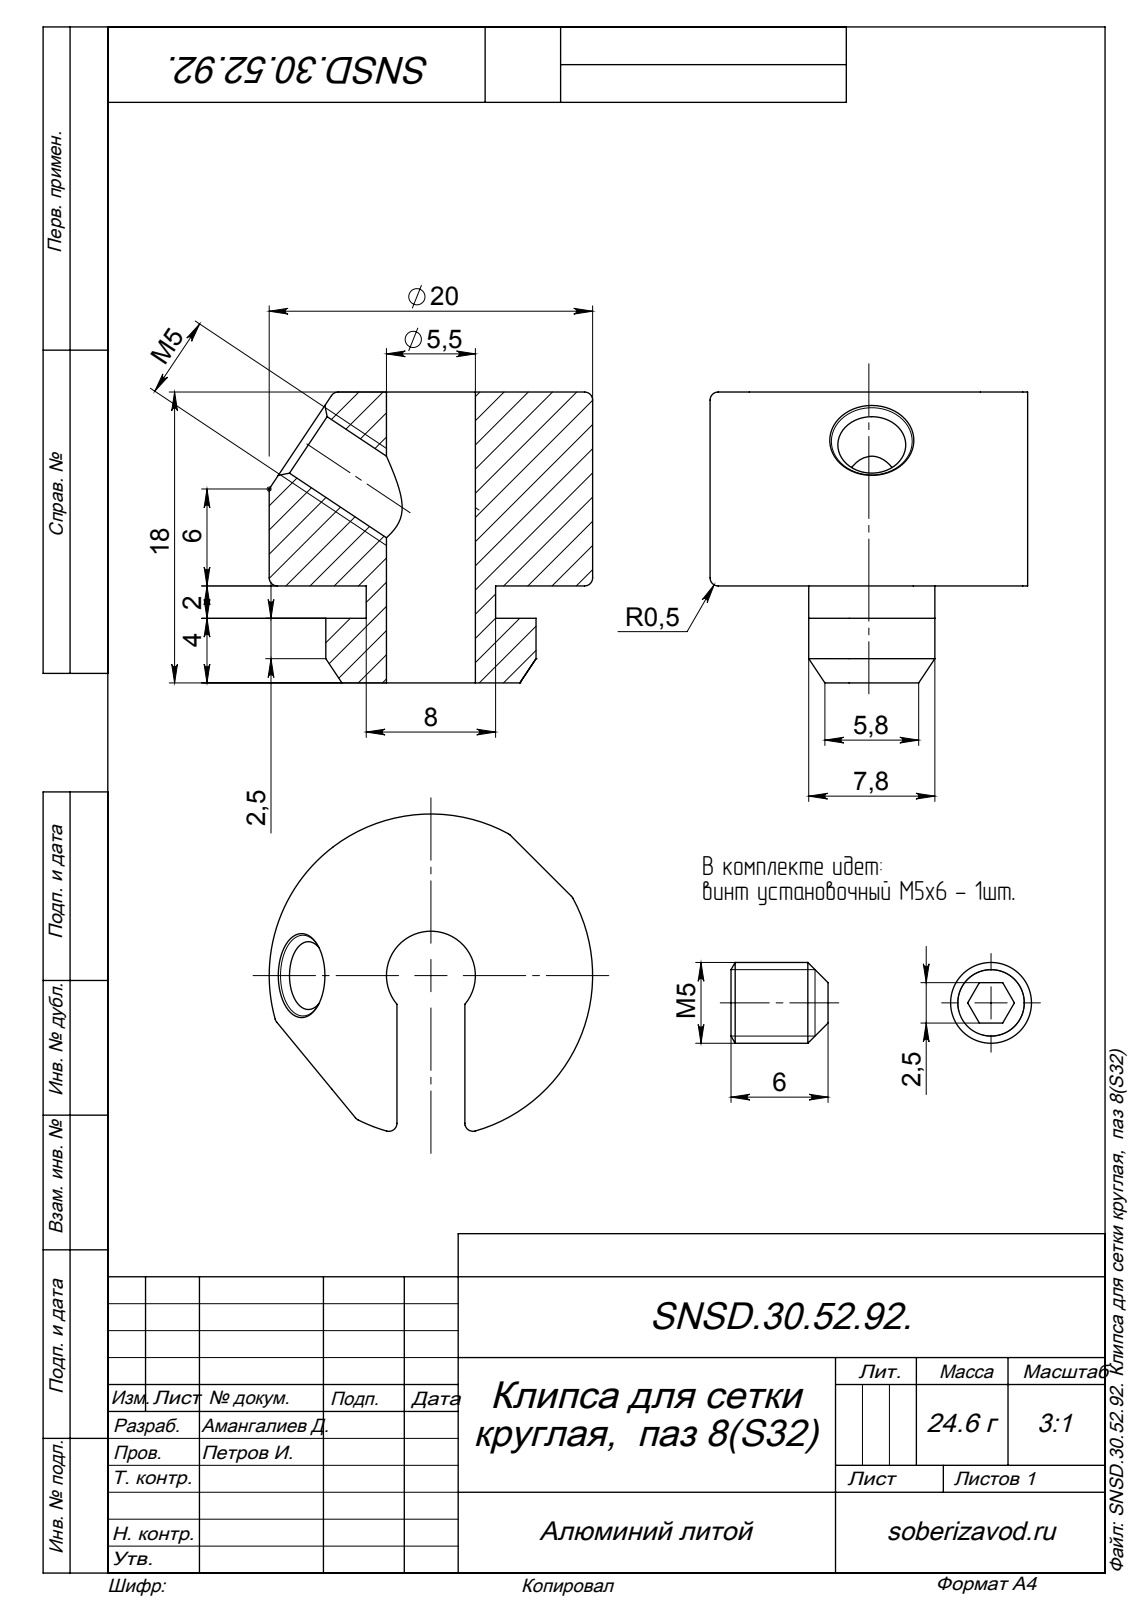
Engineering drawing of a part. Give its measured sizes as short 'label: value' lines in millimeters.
name: Установочный винт23; SNSD.30.52.92. Клипса для сетки круглая, паз 8(S32); socket set screw cup point_din; socket set screw cup point_din_DIN 916 - M5 x 6-C
written by: SolidWorks 2014 (AUTOMOTIVE_DESIGN)
unit: mm
bodies: 2 solids, 75 faces (25 planar, 25 cylindrical, 25 other)
size: 20 × 19.64 × 18
volume: 3 237 mm³; area: 2 022 mm²
holes: 1× ⌀4.2
bosses: 1× ⌀5
rounds: 12× R0.5, 2× R2.5, 2× R3, 1× R2.75, 1× R10
face distances: 12, 4.2, 2, 14, 4, 6, 18, 2.5, 4.4, 8.6
